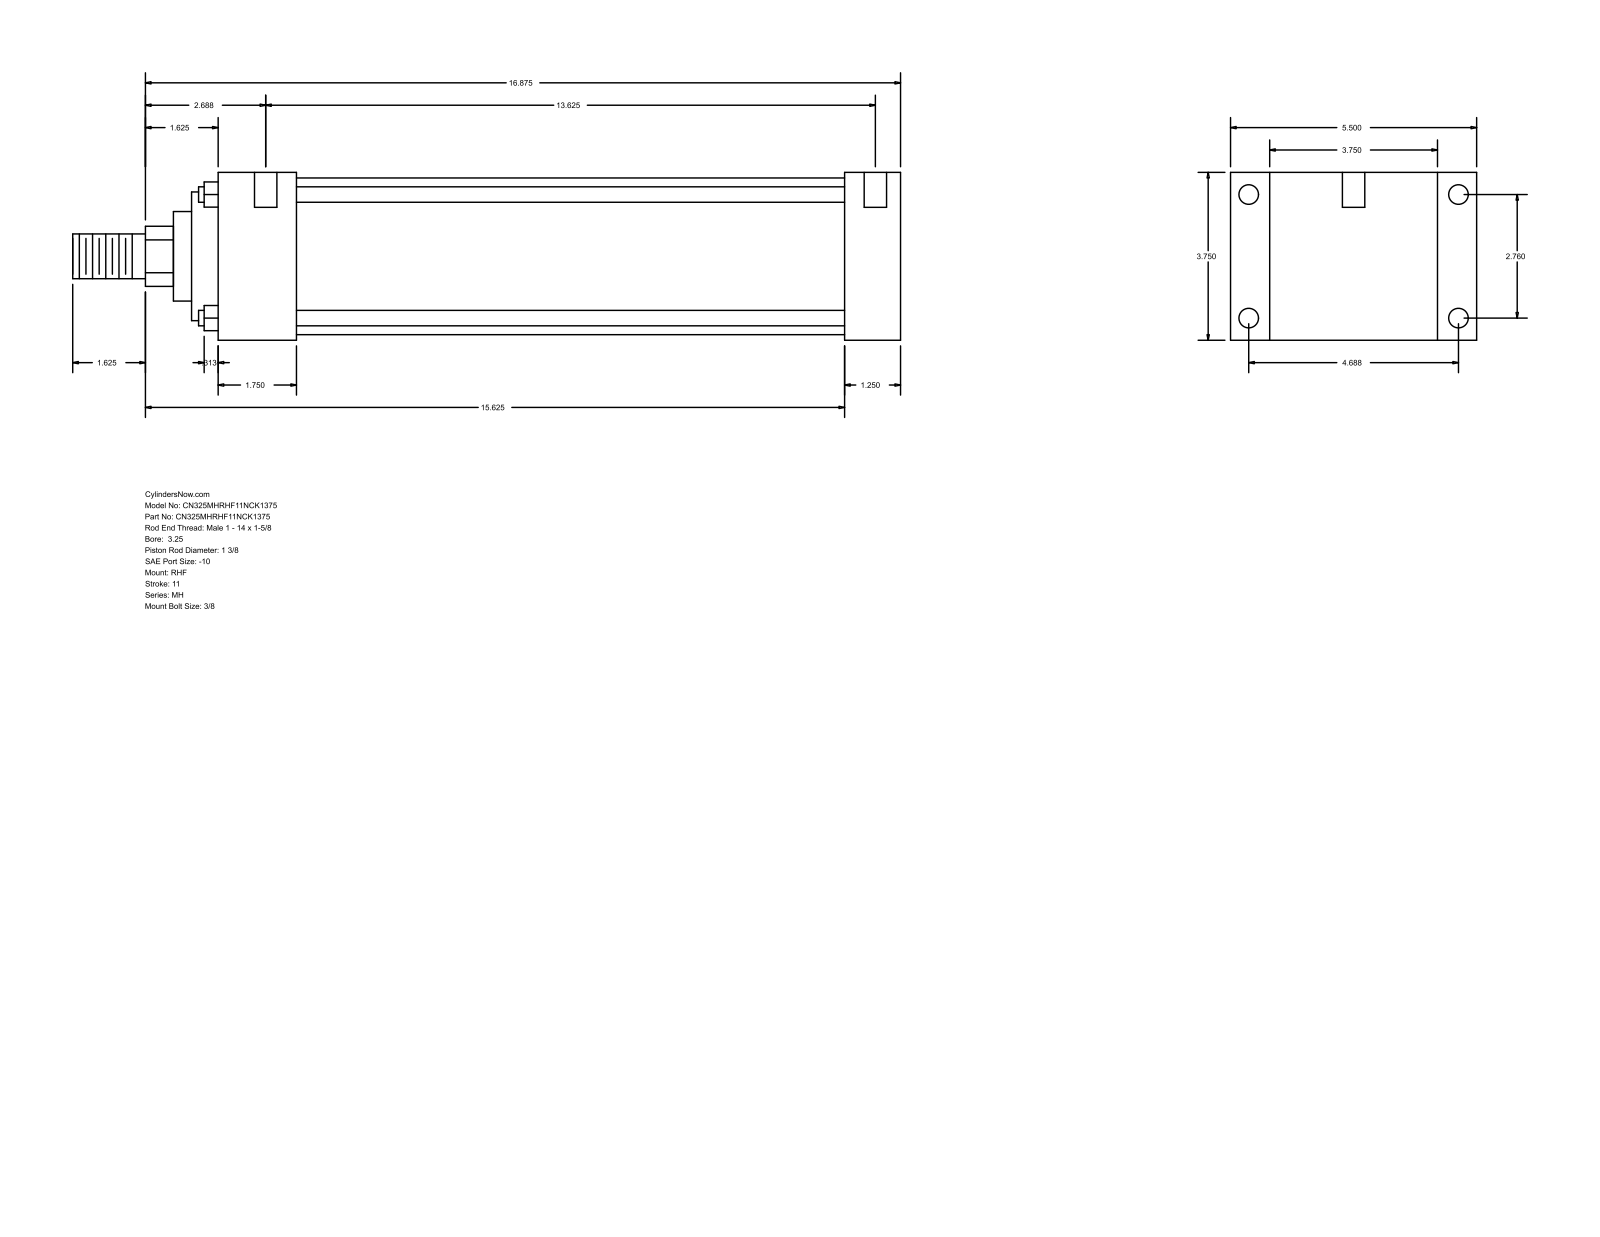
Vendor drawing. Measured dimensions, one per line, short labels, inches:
name: MH_RHF__0325_1.375
written by: GSSL Pune (CONFIG_CONTROL_DESIGN)
unit: in
bodies: 0 solids, 90 faces (61 planar, 29 cylindrical, 0 other)
size: 18.5 × 5.5 × 3.75
holes: 4× ⌀0.219, 4× ⌀0.438, 2× ⌀0.5
bosses: 4× ⌀0.345, 1× ⌀3.5, 1× ⌀2.875, 1× ⌀2, 1× ⌀1.375, 1× ⌀1
rounds: 1× R0.672
face distances: 3.75, 1.25, 0.875, 4.625, 14, 15.25, 5.5, 1.75, 12.25, 13.5
hole spacings: 2.76, 4.687, 5.439, 13.875, 0.063, 0.187, 13.625, 13.688
